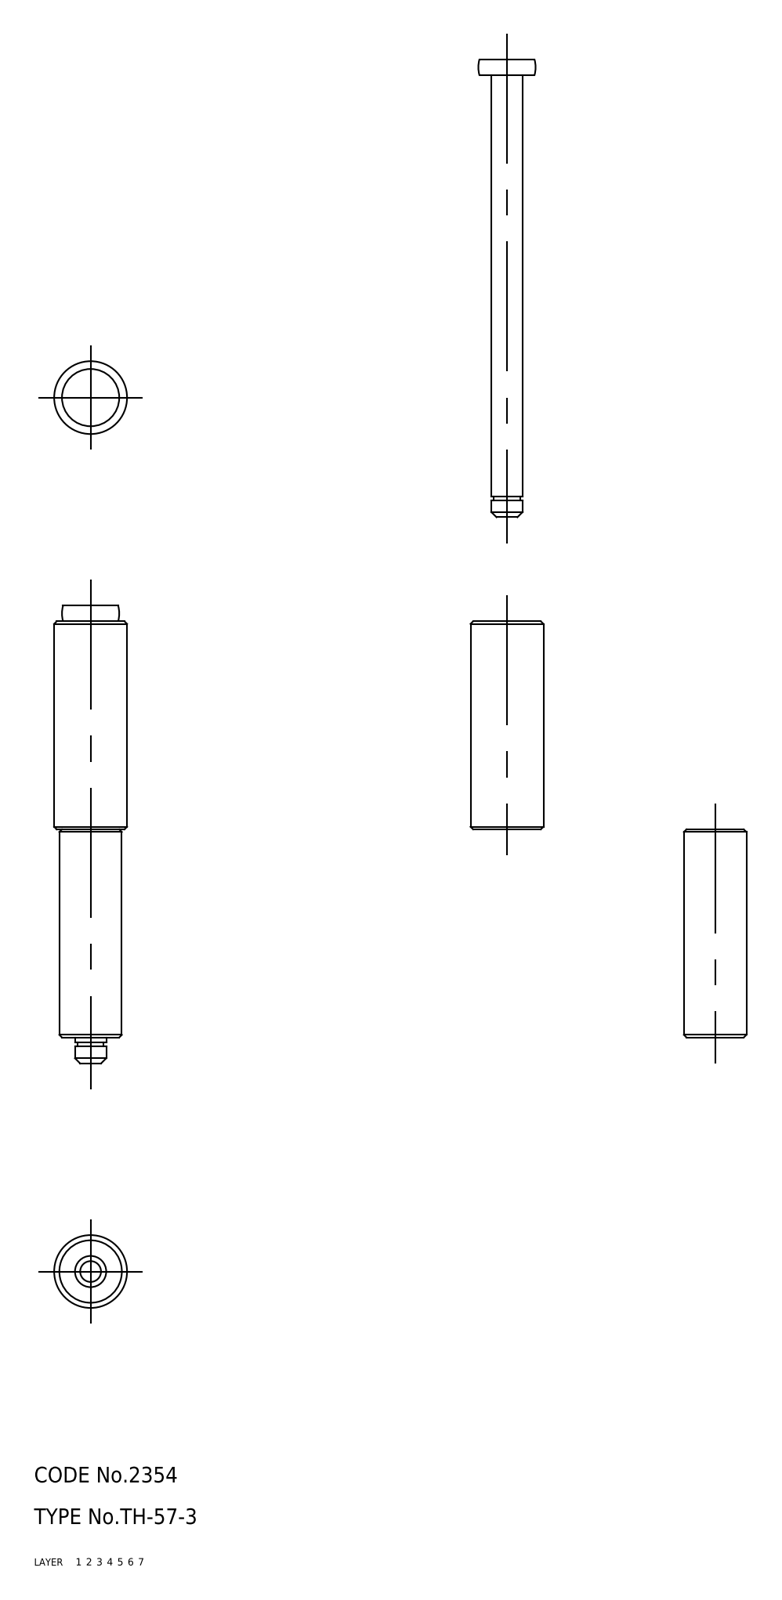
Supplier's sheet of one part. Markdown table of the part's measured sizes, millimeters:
| quantity | value |
| --- | --- |
| part name | shaft; collar_B; collar_A; TH_57_3_11681_36 |
| STEP written by | CADfix (AUTOMOTIVE_DESIGN) |
| units | millimeters |
| bodies | 3 solids, 34 faces (0 planar, 0 cylindrical, 34 other) |
| overall size | 88 × 14 × 14 |
| volume | 11 087 mm³ |
| surface area | 7 036 mm² |
